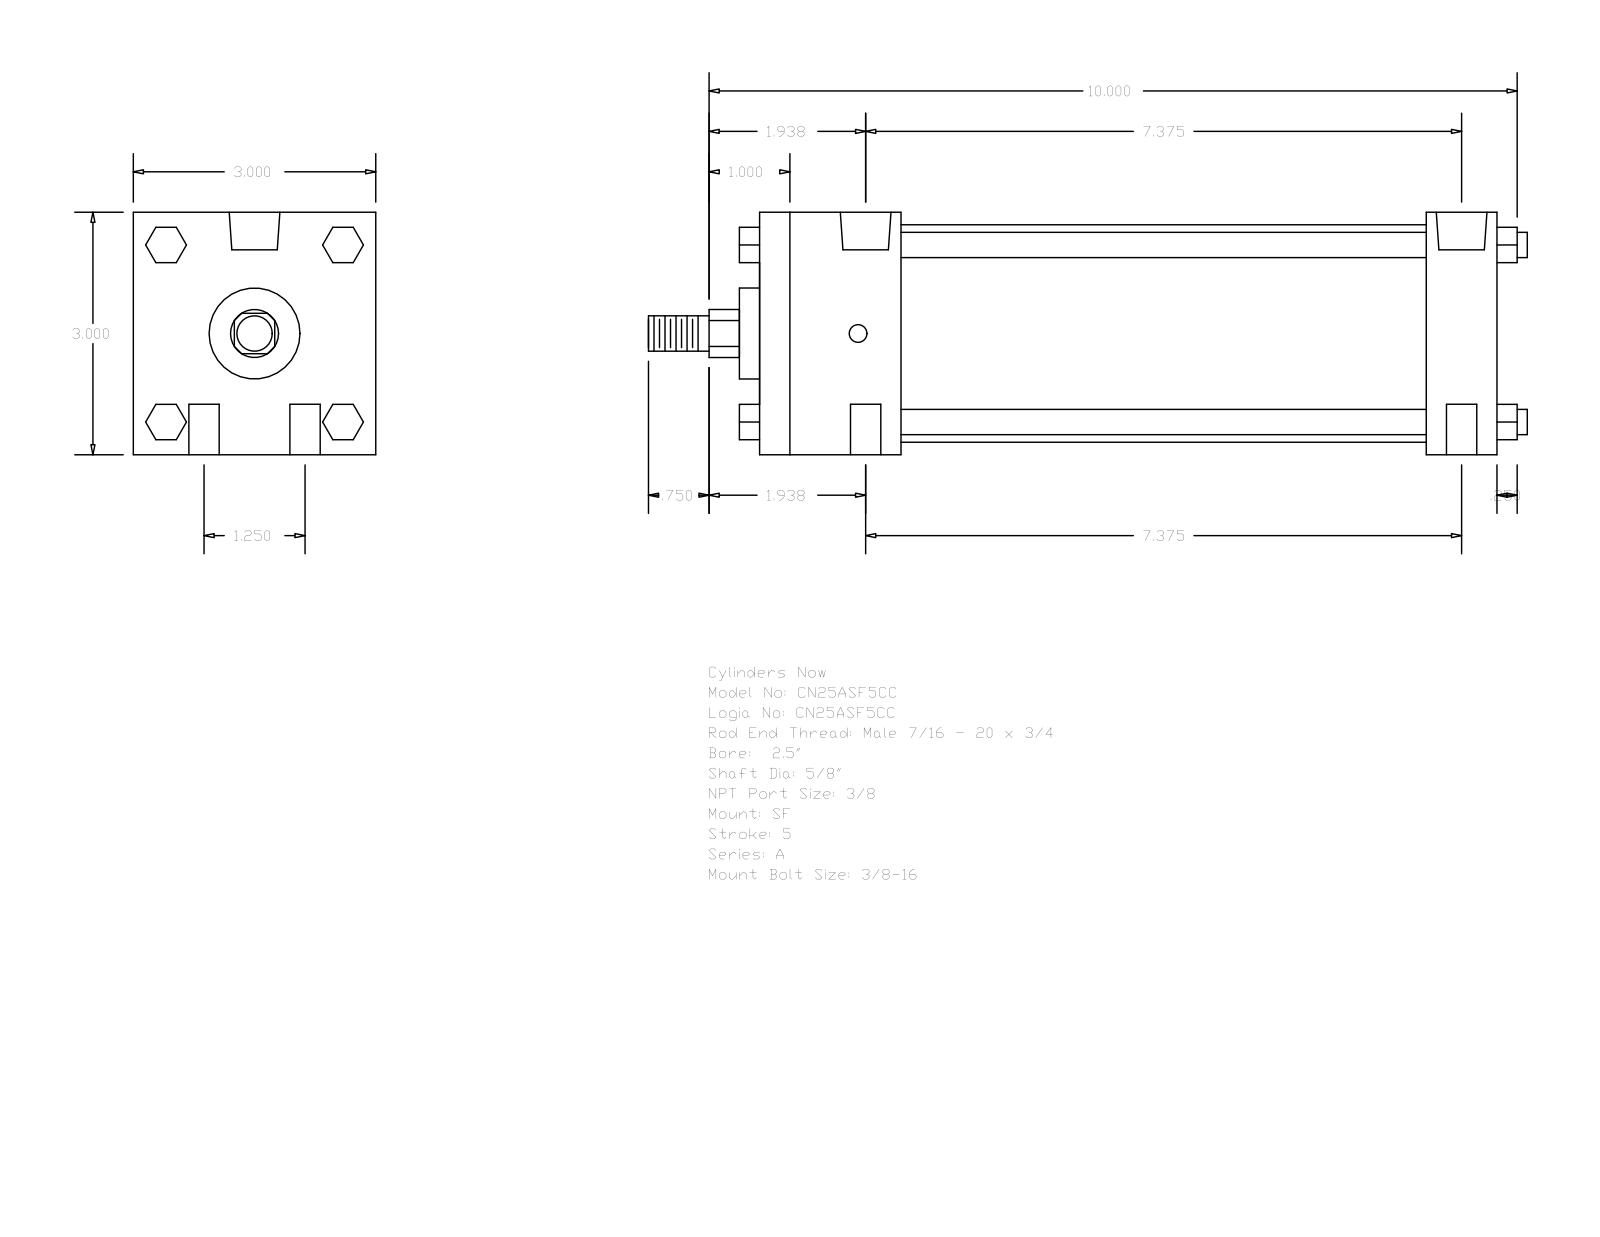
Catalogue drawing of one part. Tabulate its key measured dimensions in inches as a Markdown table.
| quantity | value |
| --- | --- |
| part name | A_SF__0250_0.625 |
| STEP written by | GSSL Pune (CONFIG_CONTROL_DESIGN) |
| units | inches |
| bodies | 0 solids, 124 faces (94 planar, 30 cylindrical, 0 other) |
| overall size | 10.875 × 3 × 3 |
| round holes (diameter × count) | 0.375 × 4, 0.219 × 2, 0.627 × 2 |
| round bosses / shafts (diameter × count) | 0.313 × 4, 2.69 × 1, 1.125 × 1, 0.625 × 1, 0.437 × 1 |
| partial cylindrical surfaces (radius × count) | 0.297 × 1 |
| main face-to-face distances | 3, 9.125, 1.75, 8.25, 0.875, 6.5, 7.375, 0.25, 9.375, 2 |
| hole center spacings | 0.625, 7.402, 7.375, 1.25, 7.48, 7.563 |
